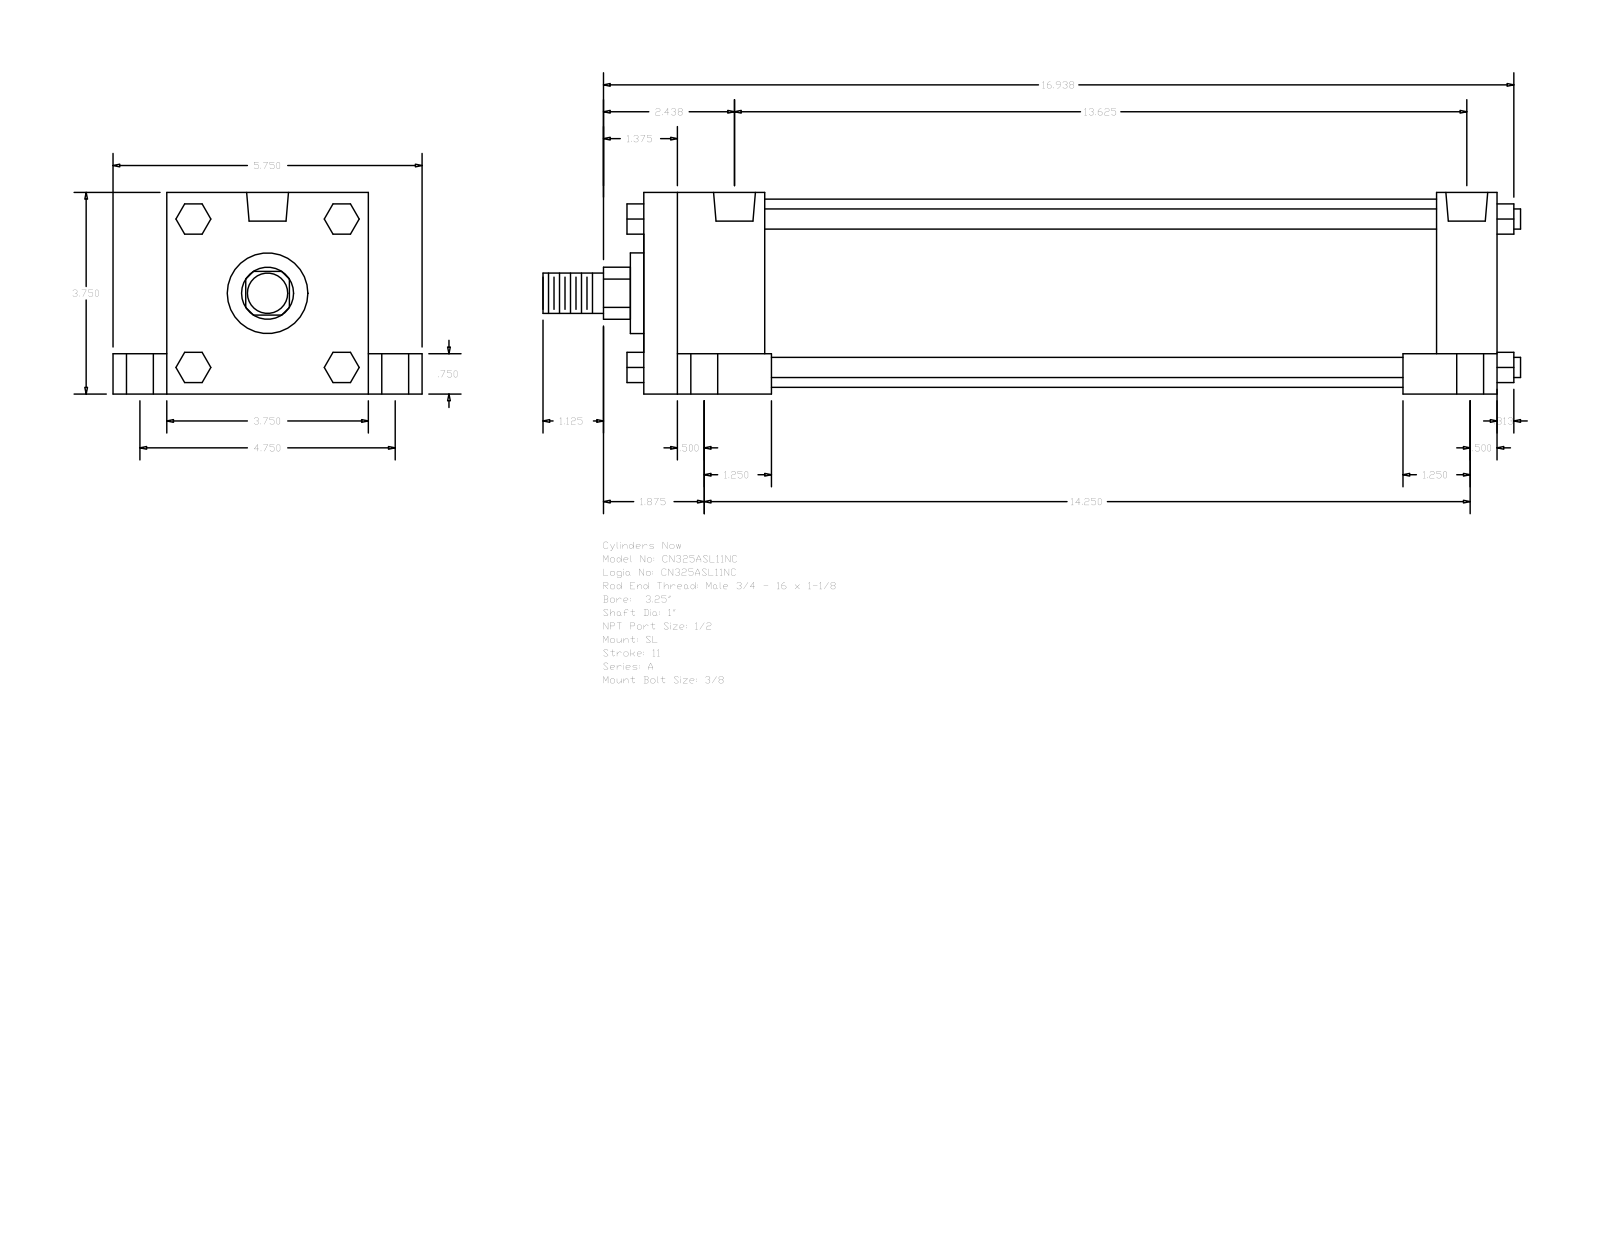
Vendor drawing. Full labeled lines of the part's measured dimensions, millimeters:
Part name (STEP PRODUCT): A_SL__0325_1
STEP written by: GSSL Pune (CONFIG_CONTROL_DESIGN)
Units: millimetres
Bodies: 0 solids, 150 faces (114 planar, 36 cylindrical, 0 other)
Overall size (bounding box): 461.96 × 146.05 × 95.25
Round holes (diameter × count): ⌀8.73 ×4, ⌀12.7 ×4, ⌀19.05 ×4, ⌀19.77 ×2
Round bosses / shafts (diameter × count): ⌀9.53 ×4, ⌀88.9 ×1, ⌀38.1 ×1, ⌀25.4 ×1, ⌀19.05 ×1
Partial cylindrical surfaces — rounded edges, fillets, slot ends (radius × count): R12.29 ×1
Main face-to-face distances: 95.24, 403.22, 19.05, 25.41, 120.65, 76.19, 28.57, 57.15, 374.65, 317.5
Hole centre spacings: 3.18, 60.35, 60.52, 62, 62.81, 120.66, 339.72, 342.9
